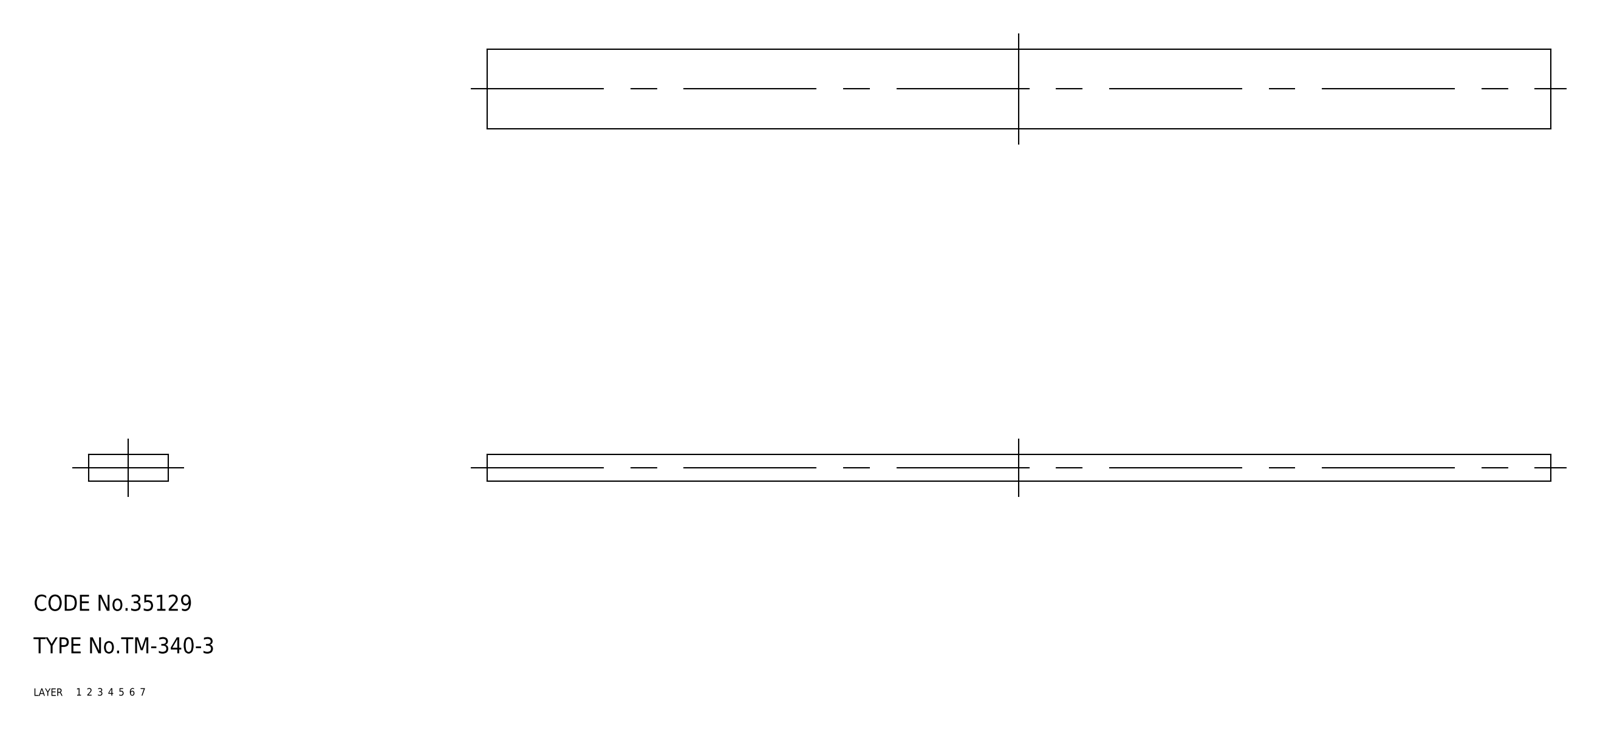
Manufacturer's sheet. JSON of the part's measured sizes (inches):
{"part_name": "TM_340_3; rubber foam", "step_written_by": "SolidWorks 2015 (AUTOMOTIVE_DESIGN)", "units": "inches", "bodies": {"solids": 1, "faces": 6, "planar": 6, "cylindrical": 0, "other": 0}, "overall_size": [7.874, 0.591, 0.197], "volume_in3": 0.915, "surface_area_in2": 12.63, "face_to_face_distances": [0.197, 0.591, 7.874]}
